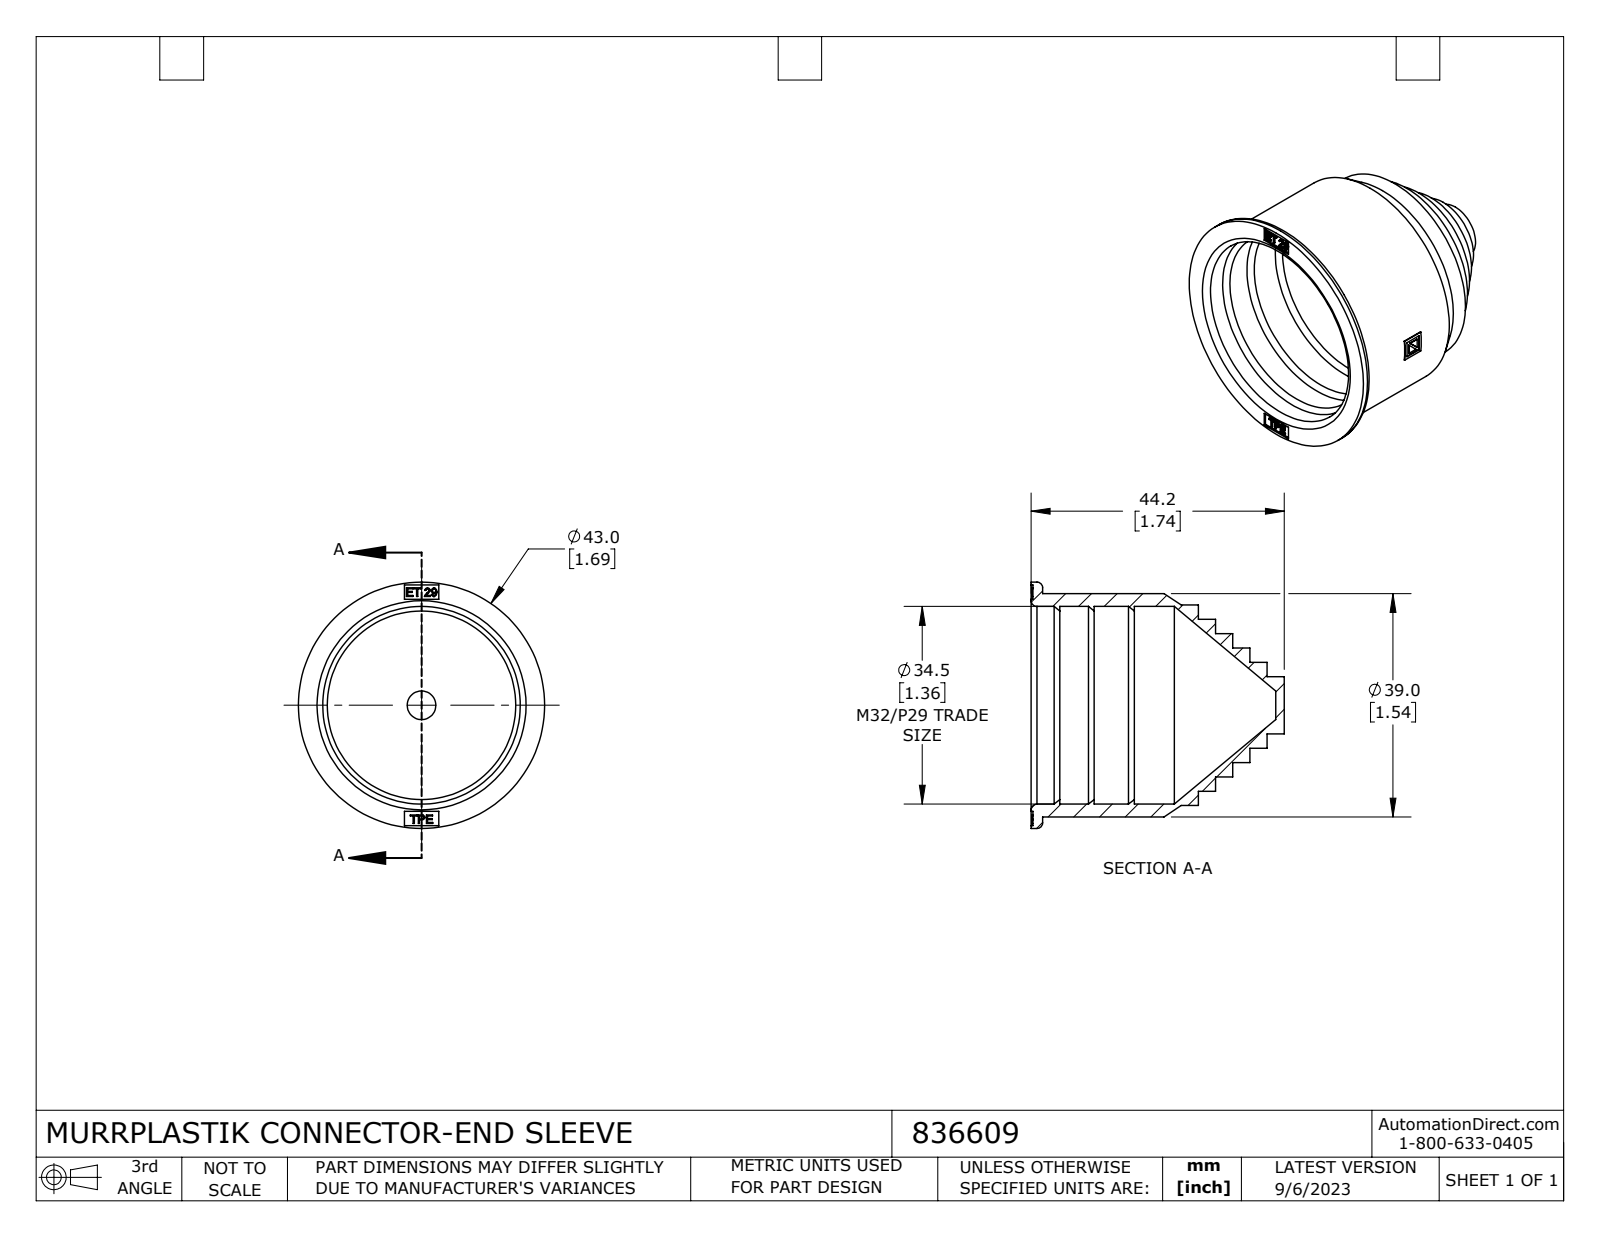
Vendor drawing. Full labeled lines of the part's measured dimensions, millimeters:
Part name (STEP PRODUCT): 836609
STEP written by: SolidWorks 2021 (CONFIG_CONTROL_DESIGN)
Units: millimetres
Bodies: 1 solid, 168 faces (98 planar, 28 cylindrical, 42 other)
Overall size (bounding box): 44.2 × 43 × 43
Volume: 9 910 mm³ · Surface area: 10 710 mm²
Round holes (diameter × count): ⌀34.5 ×1
Round bosses / shafts (diameter × count): ⌀43 ×1, ⌀39 ×1, ⌀35 ×1, ⌀30 ×1, ⌀25 ×1, ⌀20 ×1, ⌀15 ×1, ⌀10 ×1
Partial cylindrical surfaces — rounded edges, fillets, slot ends (radius × count): R19.6 ×1
Main face-to-face distances: 3, 6, 9, 27.2, 30.2, 33.2, 29.2, 32.2, 36.2, 39.2
